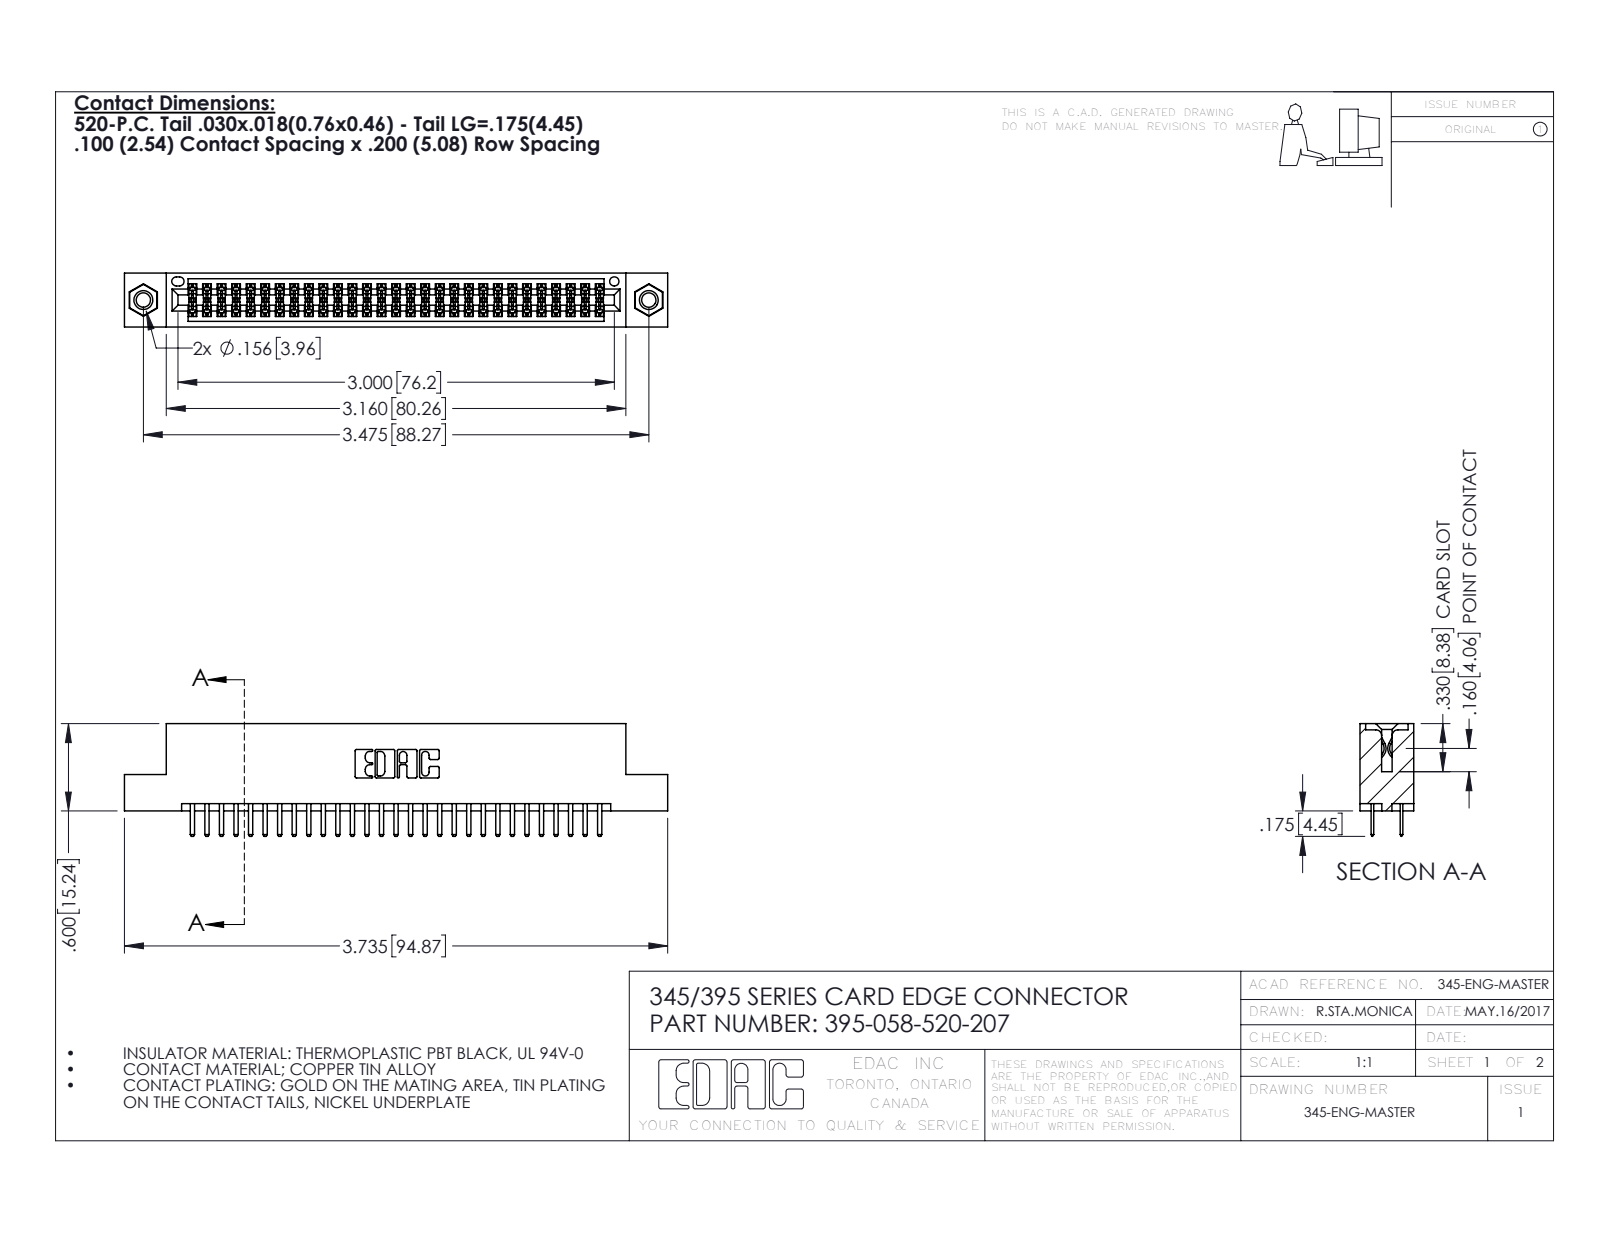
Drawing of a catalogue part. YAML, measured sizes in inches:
part_name: "345 Part_Flush Mounting Lugs - 0.156 Dia-TI; 345-250-001_345-250-005-103; 395-058-520-207; 345-292-001_345-293-120"
step_written_by: "SolidWorks 2016 (CONFIG_CONTROL_DESIGN)"
units: inches
bodies: {solids: 61, faces: 3318, planar: 2142, cylindrical: 1160, other: 16}
overall_size: [3.735, 0.775, 0.37]
volume: 0.553
surface_area: 20.32
round_holes:
  - {diameter: 0.098, count: 2}
  - {diameter: 0.125, count: 2}
  - {diameter: 0.156, count: 2}
  - {diameter: 0.064, count: 1}
round_bosses_or_shafts:
  - {diameter: 0.155, count: 2}
partial_cylinders:
  - {radius: 0.006, count: 87}
  - {radius: 0.01, count: 62}
  - {radius: 0.01, count: 22}
  - {radius: 0.007, count: 6}
  - {radius: 0.031, count: 6}
  - {radius: 0.026, count: 3}
  - {radius: 0.014, count: 2}
  - {radius: 0.019, count: 2}
face_to_face_distances: [0.072, 0.298, 0.2, 0.37, 0.098, 0.272, 0.025, 0.225, 0.022, 0.072]
hole_center_spacings: [0.27, 3.24, 3.475]
